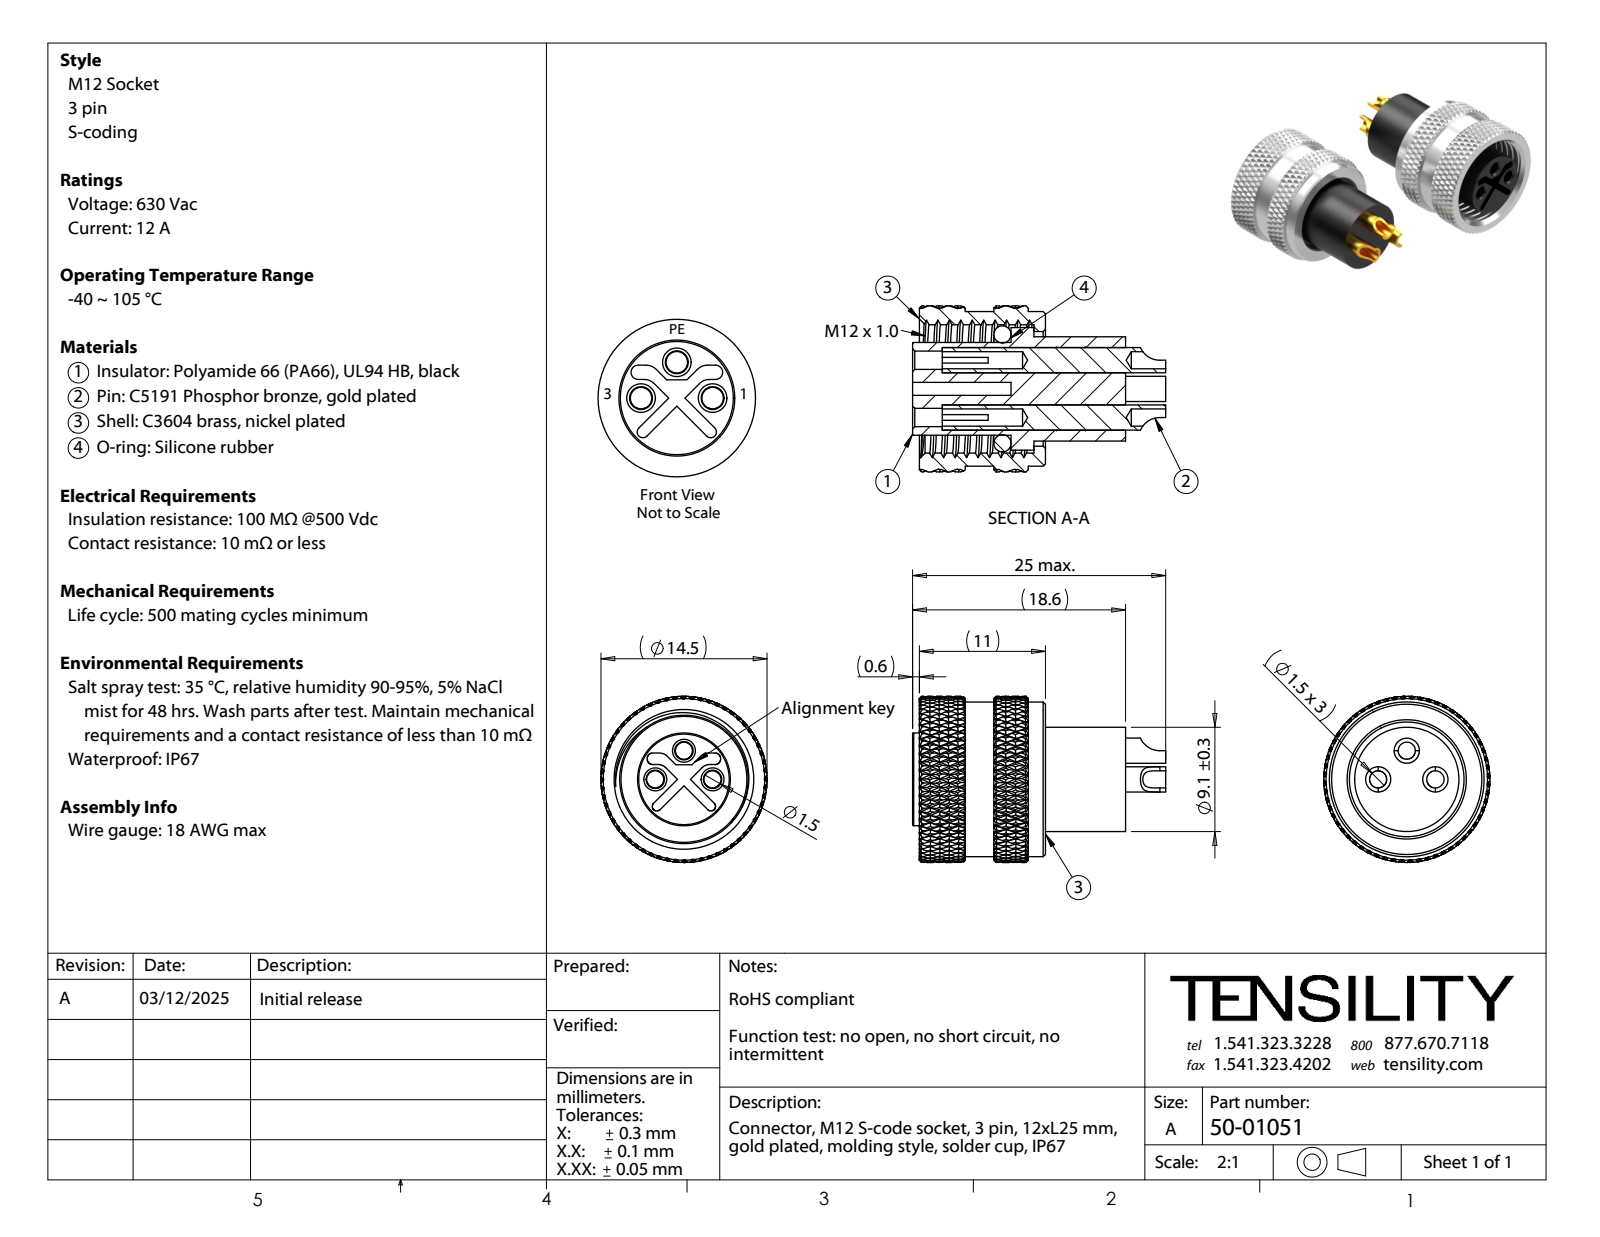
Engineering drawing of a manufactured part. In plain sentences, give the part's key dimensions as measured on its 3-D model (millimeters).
The part is named "50-01051-03; 50-01051-02; 50-01051.1; 50-01051-04 (+1 more)". Its 3-D file was written by "SolidWorks 2021 (CONFIG_CONTROL_DESIGN)". It is 6 solids with 210 faces: 67 planar, 91 cylindrical and 52 other. Overall it measures 22.1 by 14.5 by 14.5 millimeters. Its volume is 1 674 cubic millimeters and its surface area 3 190 square millimeters. Round holes: 3 of diameter 1.5, 3 of diameter 1.6, 1 of diameter 10, 1 of diameter 11.2. Round bosses or shafts: 3 of diameter 2.2, 1 of diameter 14.5, 1 of diameter 13.5, 1 of diameter 10.7, 1 of diameter 9.1, 1 of diameter 8.1. Partial cylindrical surfaces (rounded edges, fillets, slot ends): 4 of radius 1, 3 of radius 1.86, 2 of radius 0.4, 2 of radius 0.5. The main face-to-face distances are 8, 10, 2, 0.8, 7, 3, 1, 11, 18, 1.5. The hole center spacings are 2.5, 3.54, 5.
